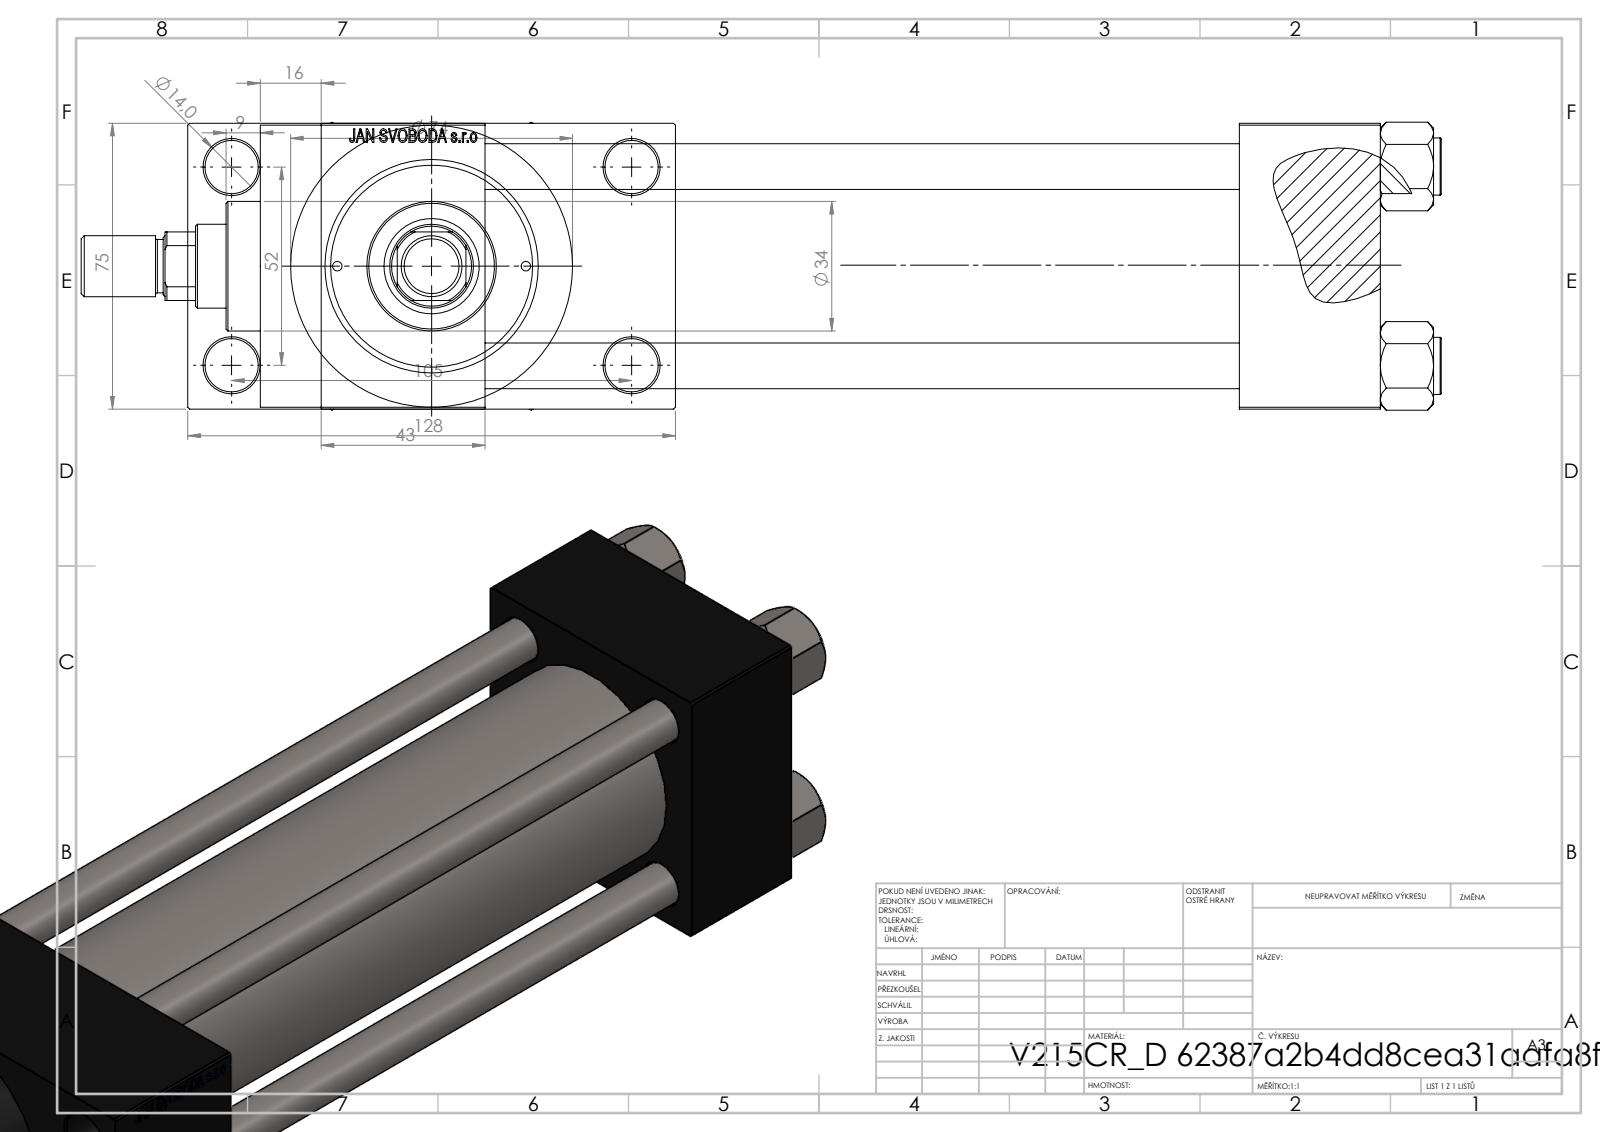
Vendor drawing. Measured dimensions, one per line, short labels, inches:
name: NUT_M5_D; V215_VC_A; ROD_END_AH; V215CR_D_Body (+2 more)
written by: SolidWorks 2019 (CONFIG_CONTROL_DESIGN)
unit: in
bodies: 12 solids, 1125 faces (503 planar, 96 cylindrical, 526 other)
size: 14.055 × 5.039 × 2.974
volume: 60.3 in³; area: 380.6 in²
holes: 4× ⌀0.472, 4× ⌀0.551, 2× ⌀0.098, 2× ⌀0.276, 2× ⌀0.825, 2× ⌀1.181, 1× ⌀0.413, 1× ⌀0.866, 1× ⌀0.984, 1× ⌀1.614, 1× ⌀1.969, 1× ⌀2.087
bosses: 4× ⌀0.591, 1× ⌀2.913, 1× ⌀2.205, 1× ⌀1.339, 1× ⌀0.63, 1× ⌀0.551
rounds: 1× R0.413
face distances: 2.953, 7.795, 1.457, 9.252, 1.043, 10.945, 9.488, 1.693, 3.996, 0.63
hole spacings: 1.031, 1.037, 1.456, 1.497, 2.059, 2.253, 2.3, 2.307
